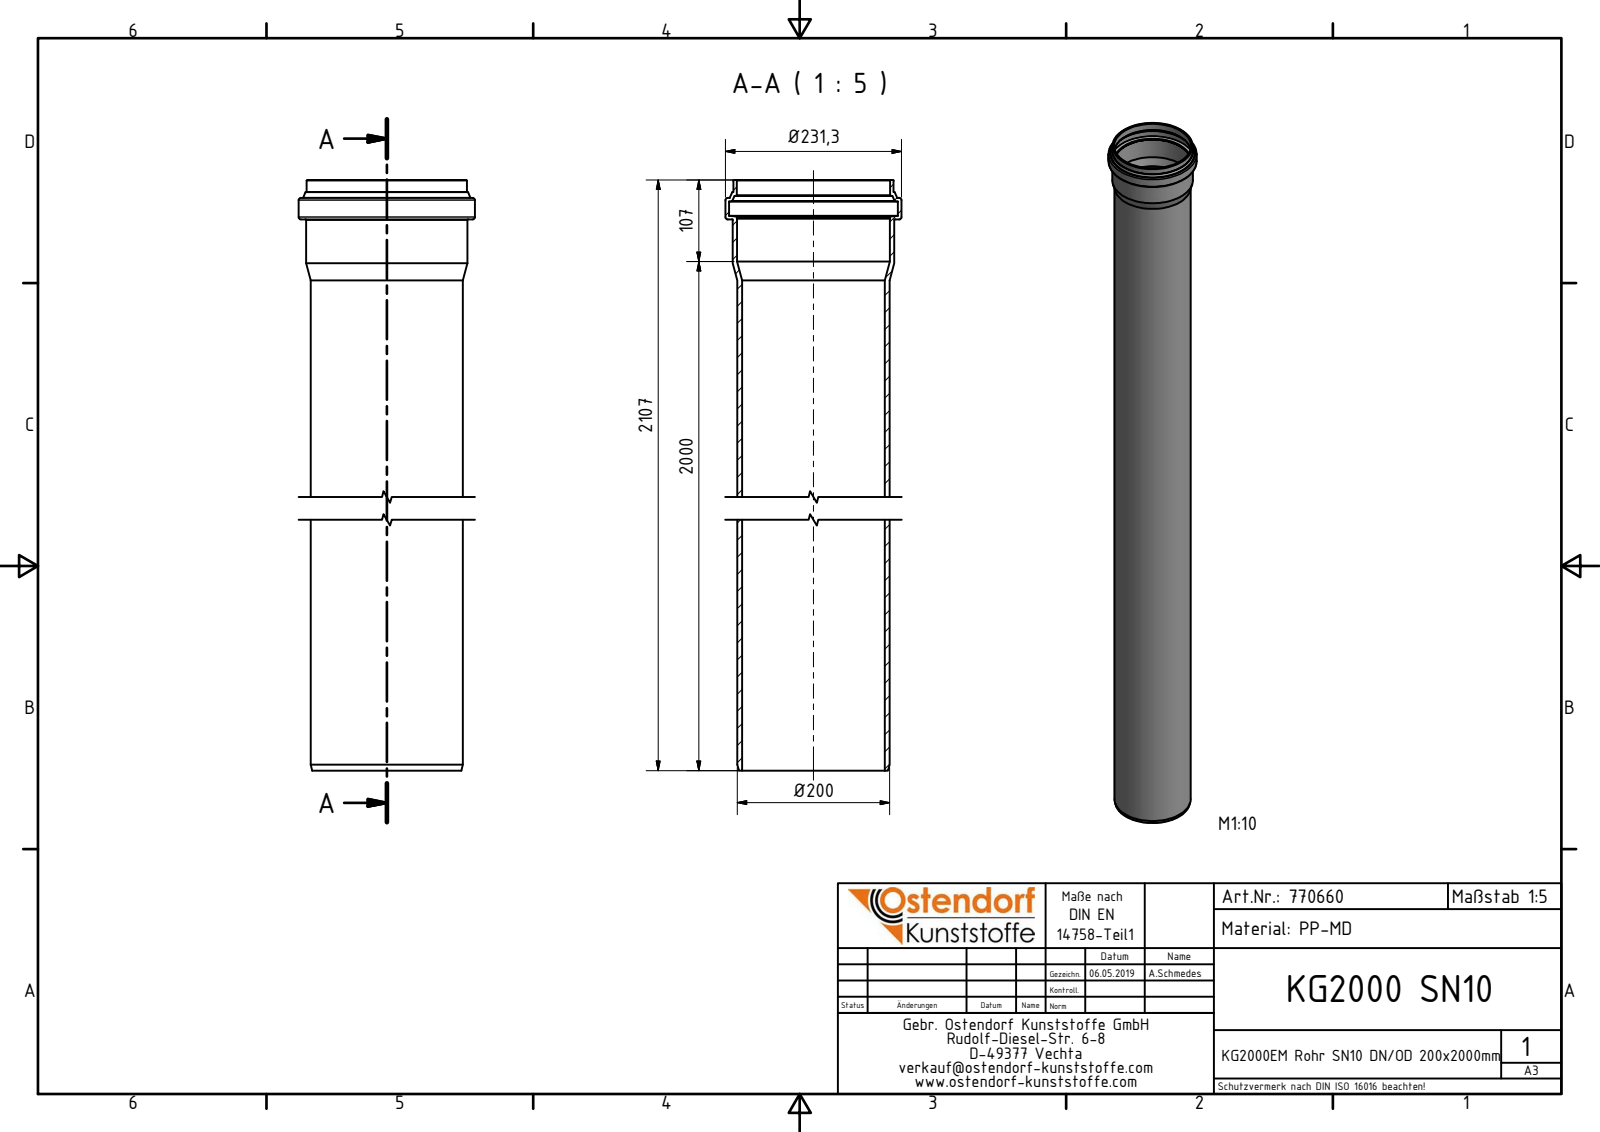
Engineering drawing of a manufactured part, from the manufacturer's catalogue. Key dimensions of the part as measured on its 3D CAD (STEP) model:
Part name (STEP PRODUCT): 770660 KG2000EM Rohr SN10 DN-OD200x2000
STEP written by: Autodesk Inventor 2016 (AUTOMOTIVE_DESIGN)
Units: millimetres
Bodies: 1 solid, 37 faces (6 planar, 9 cylindrical, 22 other)
Overall size (bounding box): 2107 × 231.3 × 231.3
Volume: 7 965 000 mm³ · Surface area: 2 605 000 mm²
Round holes (diameter × count): ⌀187.6 ×1, ⌀200.8 ×1, ⌀201 ×1, ⌀221.9 ×1
Round bosses / shafts (diameter × count): ⌀231.3 ×1, ⌀212 ×1, ⌀210.4 ×1, ⌀200 ×1
Main face-to-face distances: 2055.3, 2083.5, 28.2, 2107, 51.7, 23.5, 2090.97, 35.67, 7.47, 16.03
